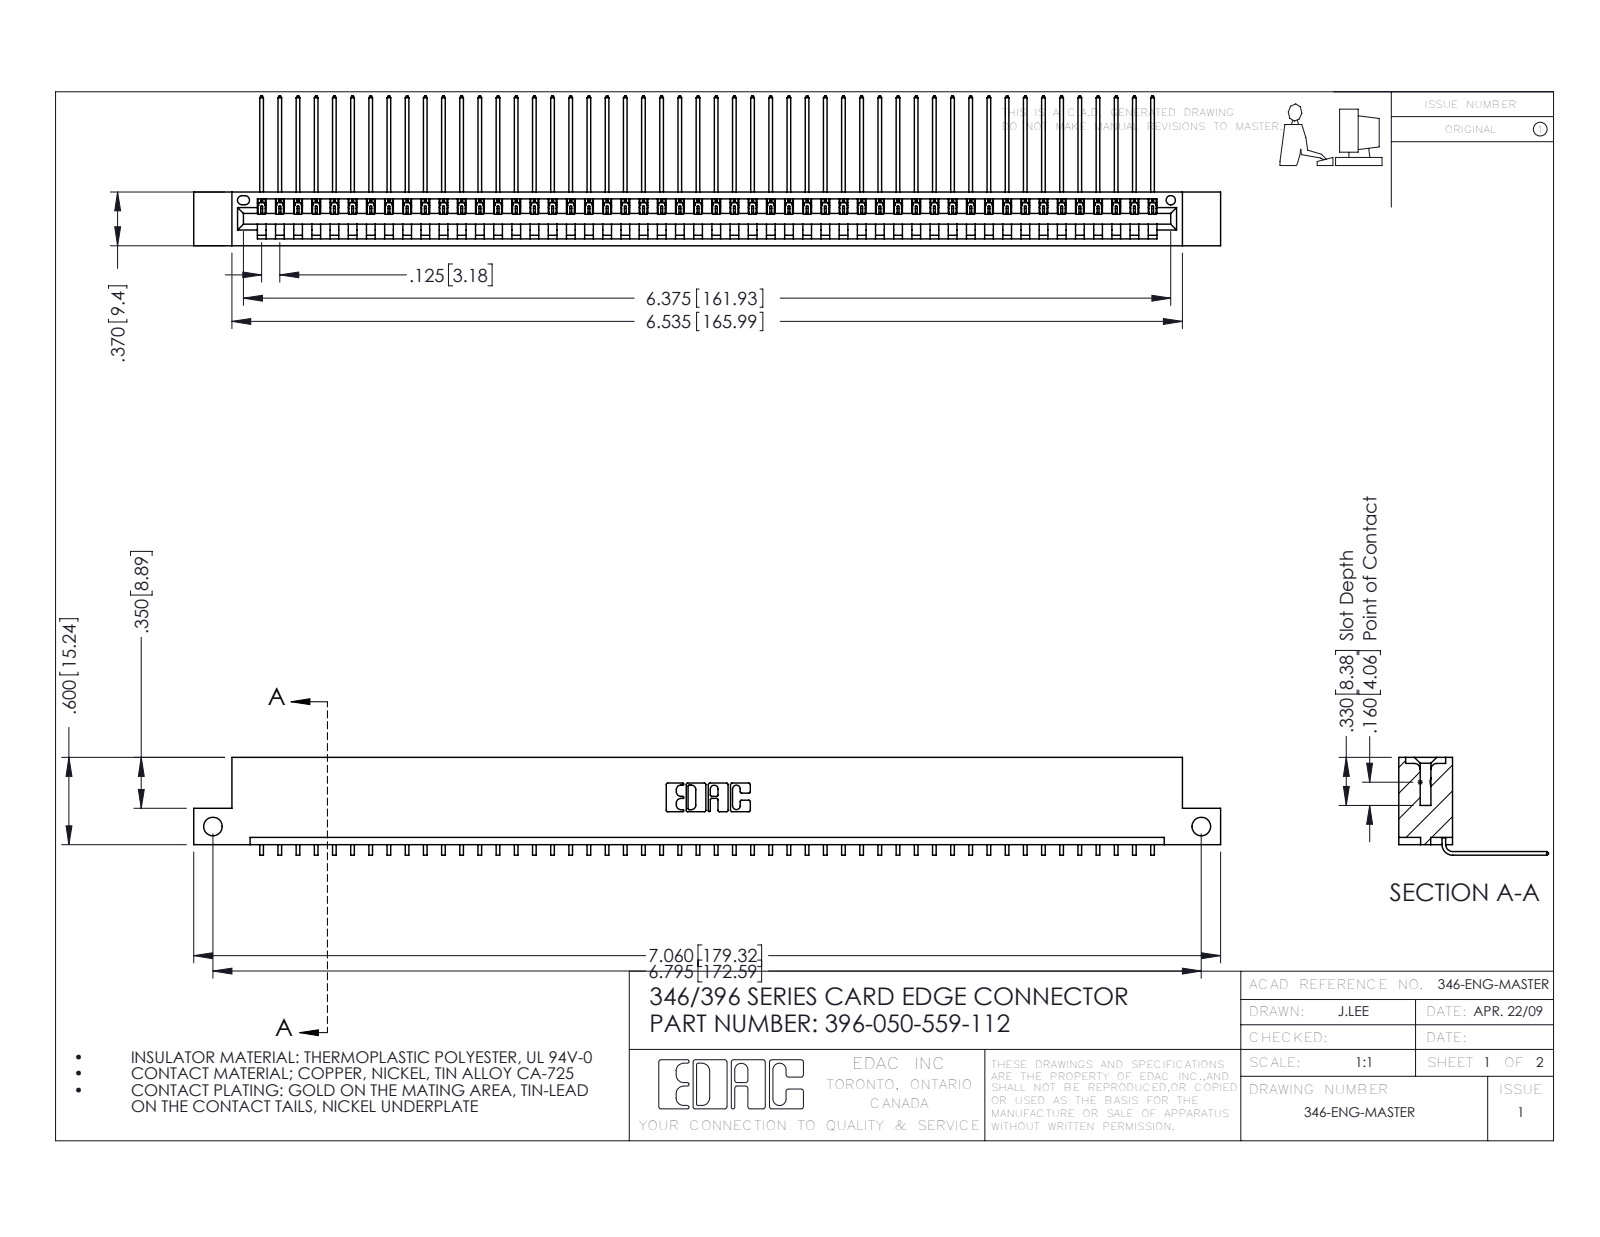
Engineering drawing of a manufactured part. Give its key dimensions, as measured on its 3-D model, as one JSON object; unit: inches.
{"part_name": "346 Part_Flush Mounting Lugs - Side Mount; 396-050-559-112; 345-292-001_558 559 Tail - 1", "step_written_by": "SolidWorks 2016 (CONFIG_CONTROL_DESIGN)", "units": "inches", "bodies": {"solids": 51, "faces": 3122, "planar": 2176, "cylindrical": 946, "other": 0}, "overall_size": [7.06, 1.03, 0.673], "volume_in3": 1.056, "surface_area_in2": 34.96, "round_holes": [[0.128, 2], [0.064, 1]], "partial_cylinders_radius": [[0.006, 100], [0.01, 22], [0.007, 6], [0.031, 6], [0.026, 3], [0.031, 2], [0.04, 2], [0.014, 1]], "face_to_face_distances": [0.048, 0.322, 0.37, 0.25, 0.025, 0.072, 0.298, 0.148, 0.222, 0.1], "hole_center_spacings": [6.795]}
